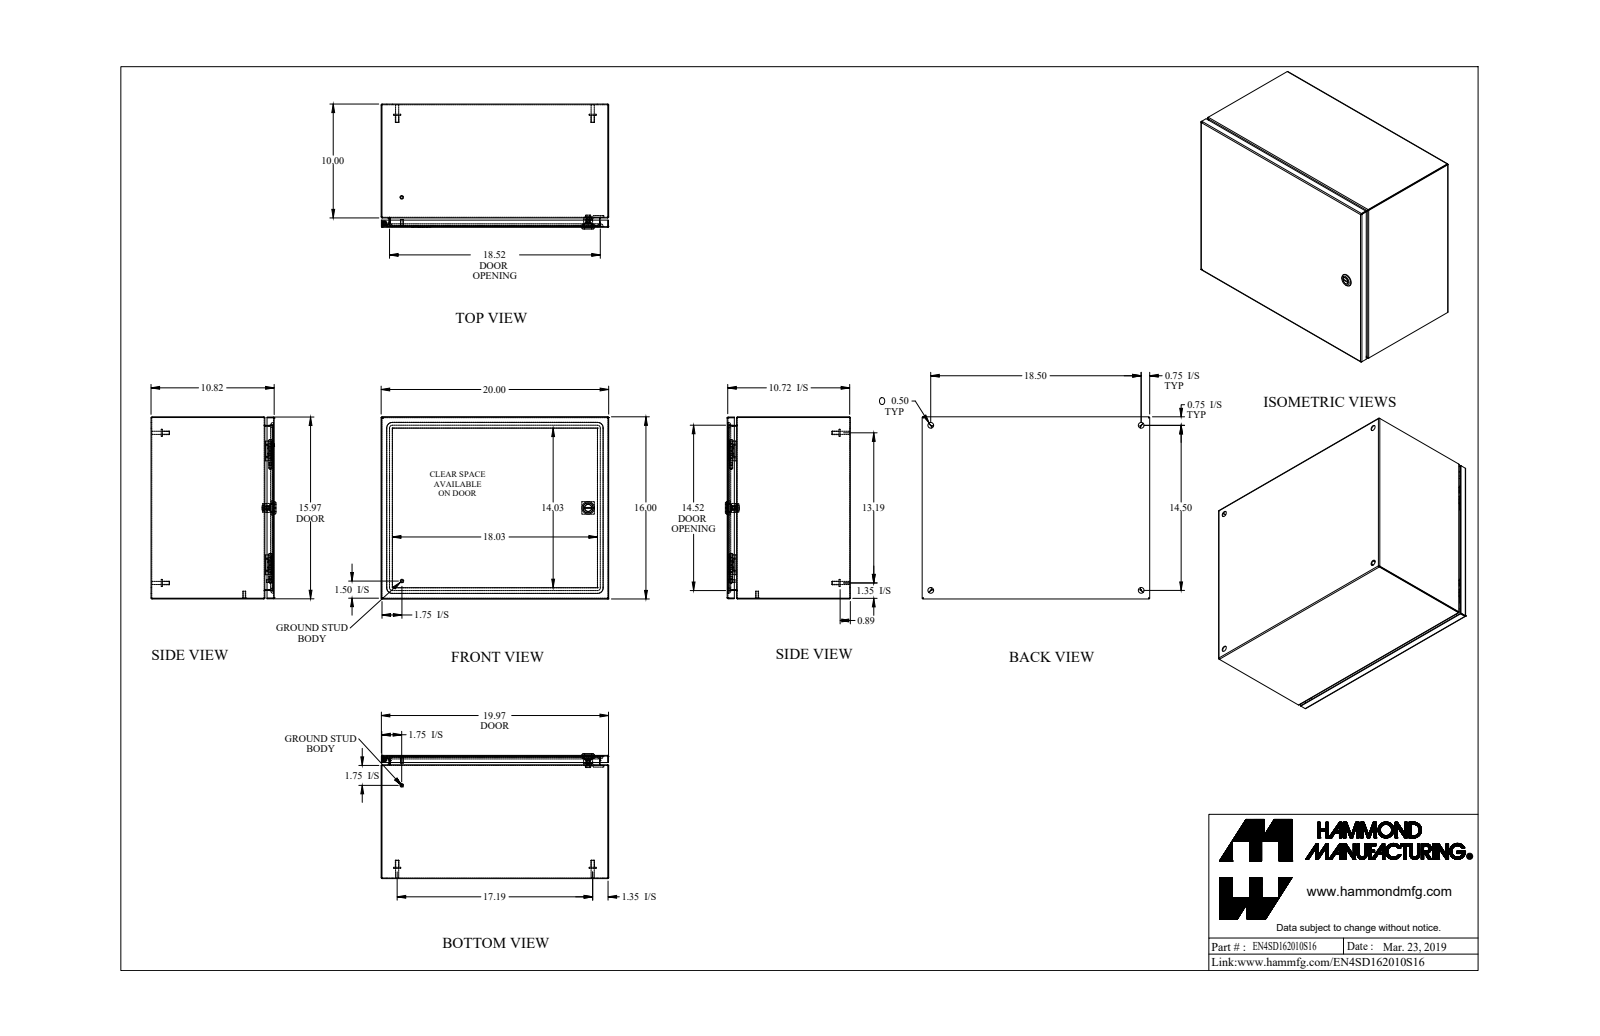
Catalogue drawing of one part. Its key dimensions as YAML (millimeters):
part_name: "EN4SD162010S16_Default"
step_written_by: "SolidWorks 2019 (CONFIG_CONTROL_DESIGN)"
units: millimeters
bodies: {solids: 22, faces: 656, planar: 303, cylindrical: 211, other: 142}
overall_size: [508, 406.4, 278.9]
volume: 1518000
surface_area: 2041000
round_holes:
  - {diameter: 12.7, count: 5}
  - {diameter: 4.4, count: 1}
  - {diameter: 5, count: 1}
  - {diameter: 6.1, count: 1}
  - {diameter: 6.1, count: 1}
  - {diameter: 9.8, count: 1}
  - {diameter: 16, count: 1}
  - {diameter: 19.5, count: 1}
round_bosses_or_shafts:
  - {diameter: 8, count: 6}
  - {diameter: 15.9, count: 5}
  - {diameter: 7, count: 4}
  - {diameter: 6.4, count: 2}
  - {diameter: 27.9, count: 1}
  - {diameter: 19.9, count: 1}
  - {diameter: 13.3, count: 1}
  - {diameter: 12.1, count: 1}
partial_cylinders:
  - {radius: 0.7, count: 21}
  - {radius: 2.2, count: 21}
  - {radius: 4.8, count: 12}
  - {radius: 0.2, count: 4}
  - {radius: 1.6, count: 4}
  - {radius: 6.4, count: 4}
  - {radius: 12.7, count: 4}
  - {radius: 3.2, count: 2}
face_to_face_distances: [1.4, 405, 1.4, 272, 273.4, 273.4, 274.9, 506.6, 403.5, 406.4]
hole_center_spacings: [186.1, 368.3, 469.9, 479.8, 597.1]
